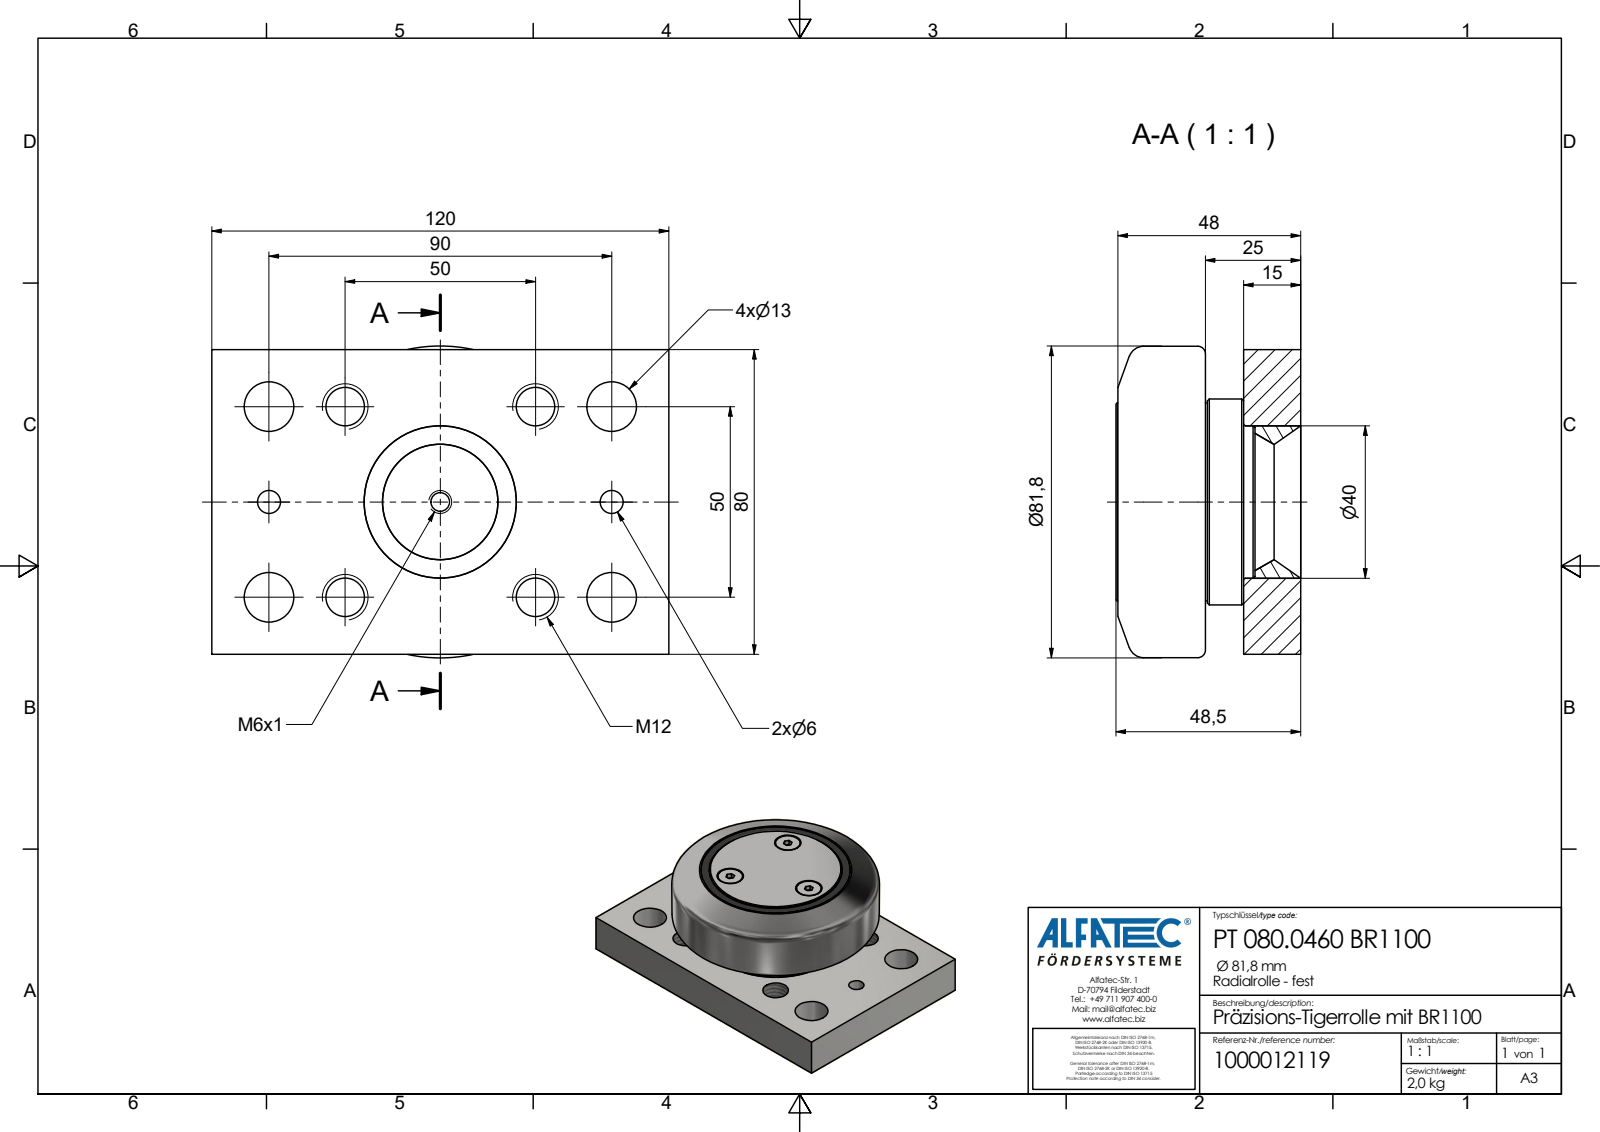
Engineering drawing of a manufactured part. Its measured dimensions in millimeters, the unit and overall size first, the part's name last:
Units: millimetres
Overall size (bounding box): 120 × 81.8 × 48.5
Round holes (diameter × count): ⌀10.11 ×4, ⌀13 ×4, ⌀10.4 ×3, ⌀6 ×2, ⌀4.92 ×1
Round bosses / shafts (diameter × count): ⌀9.75 ×3, ⌀54 ×1, ⌀52 ×1
Main face-to-face distances: 15, 25, 10, 23.5, 48.5, 33.5, 80, 120, 0.5, 48
Hole centre spacings: 50, 20, 25, 32.02, 35.36, 51.48, 53.85, 70
Volume: 262 126 mm³ · Surface area: 41 775 mm²
Bodies: 1 solid, 67 faces (39 planar, 20 cylindrical, 8 other)
Part name (STEP PRODUCT): PT 080.0460 BR1100_Kontur
STEP written by: Autodesk Inventor 2020 (AP242_MANAGED_MODEL_BASED_3D_ENGINEERING_MIM_LF)
